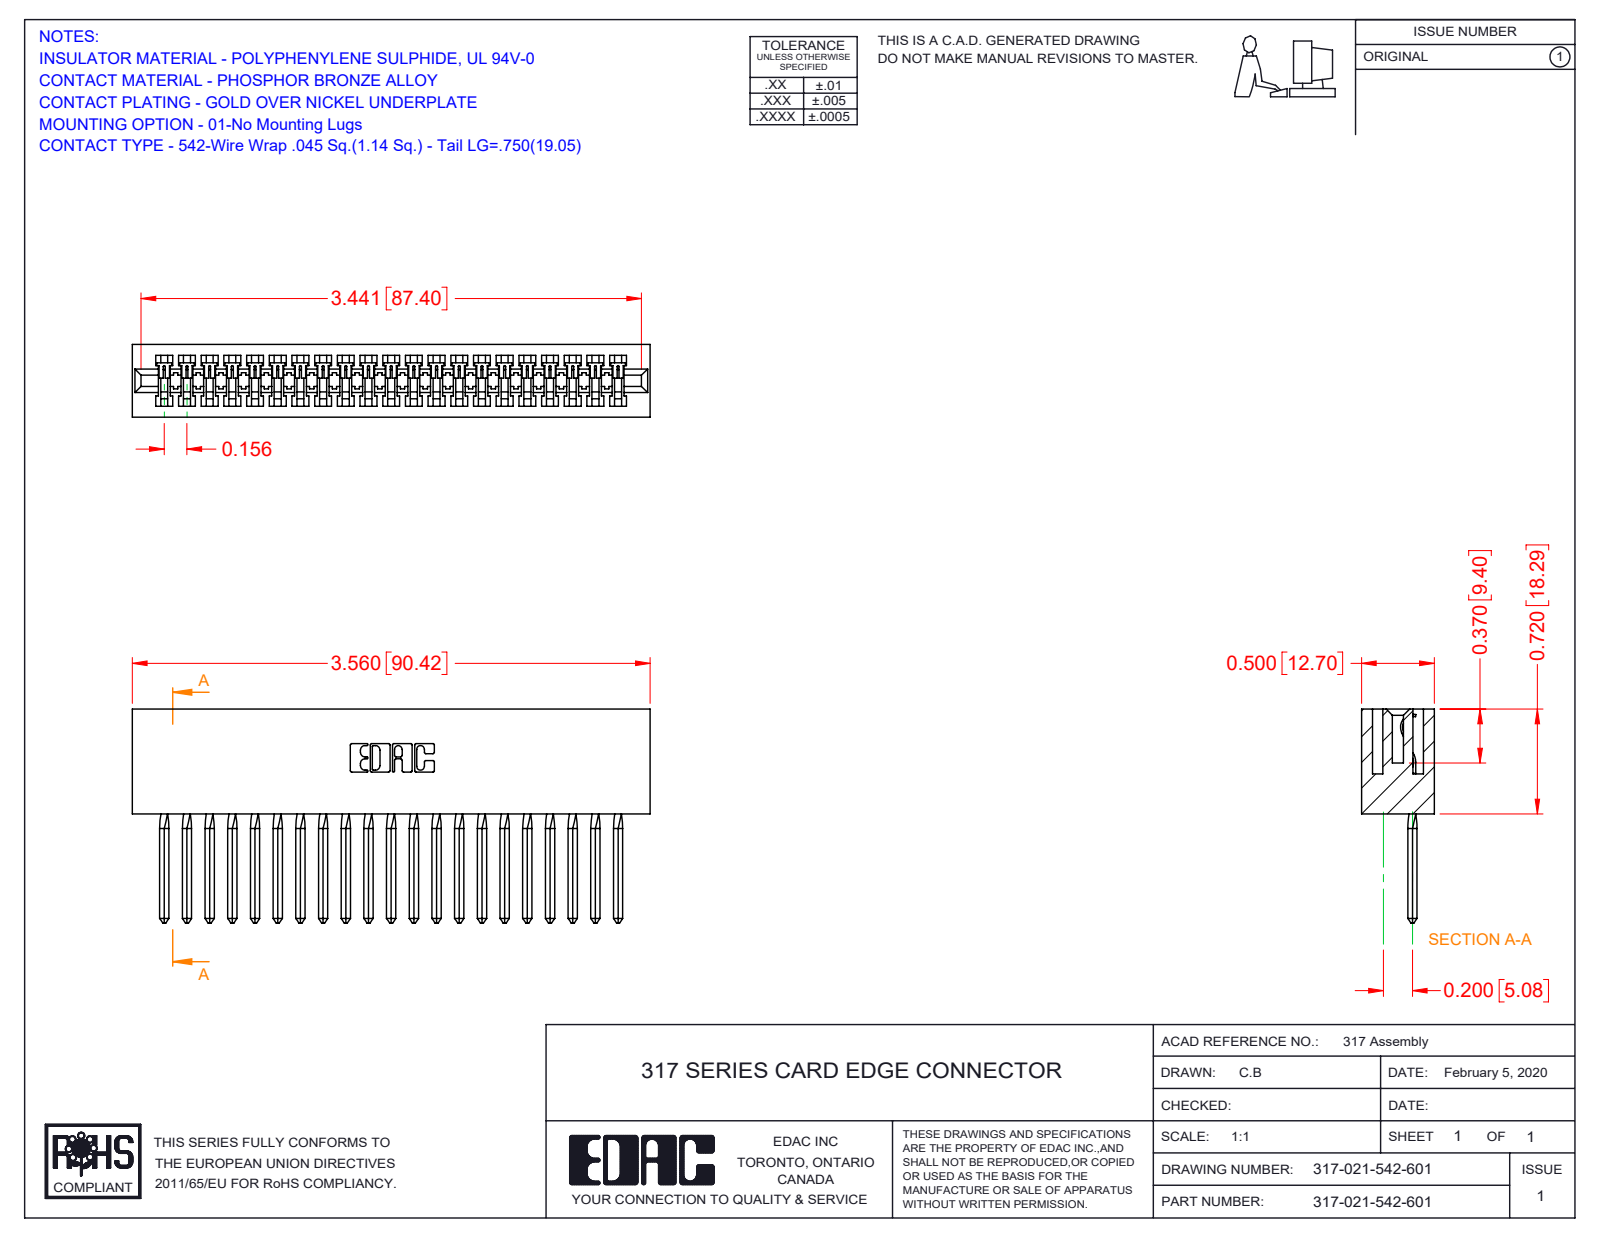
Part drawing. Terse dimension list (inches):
name: 317 Part_Lugless; 317-290-003_542; 317-021-542-601
written by: SolidWorks 2016 (CONFIG_CONTROL_DESIGN)
unit: in
bodies: 22 solids, 1665 faces (1394 planar, 187 cylindrical, 84 other)
size: 3.56 × 1.47 × 0.5
volume: 0.915 in³; area: 27.69 in²
rounds: 42× R0.006, 22× R0.01, 6× R0.007, 6× R0.031, 3× R0.026, 1× R0.074, 1× R0.089, 1× R0.1
face distances: 0.5, 0.075, 0.425, 0.35, 0.11, 0.136, 0.72, 0.211, 0.289, 0.213
